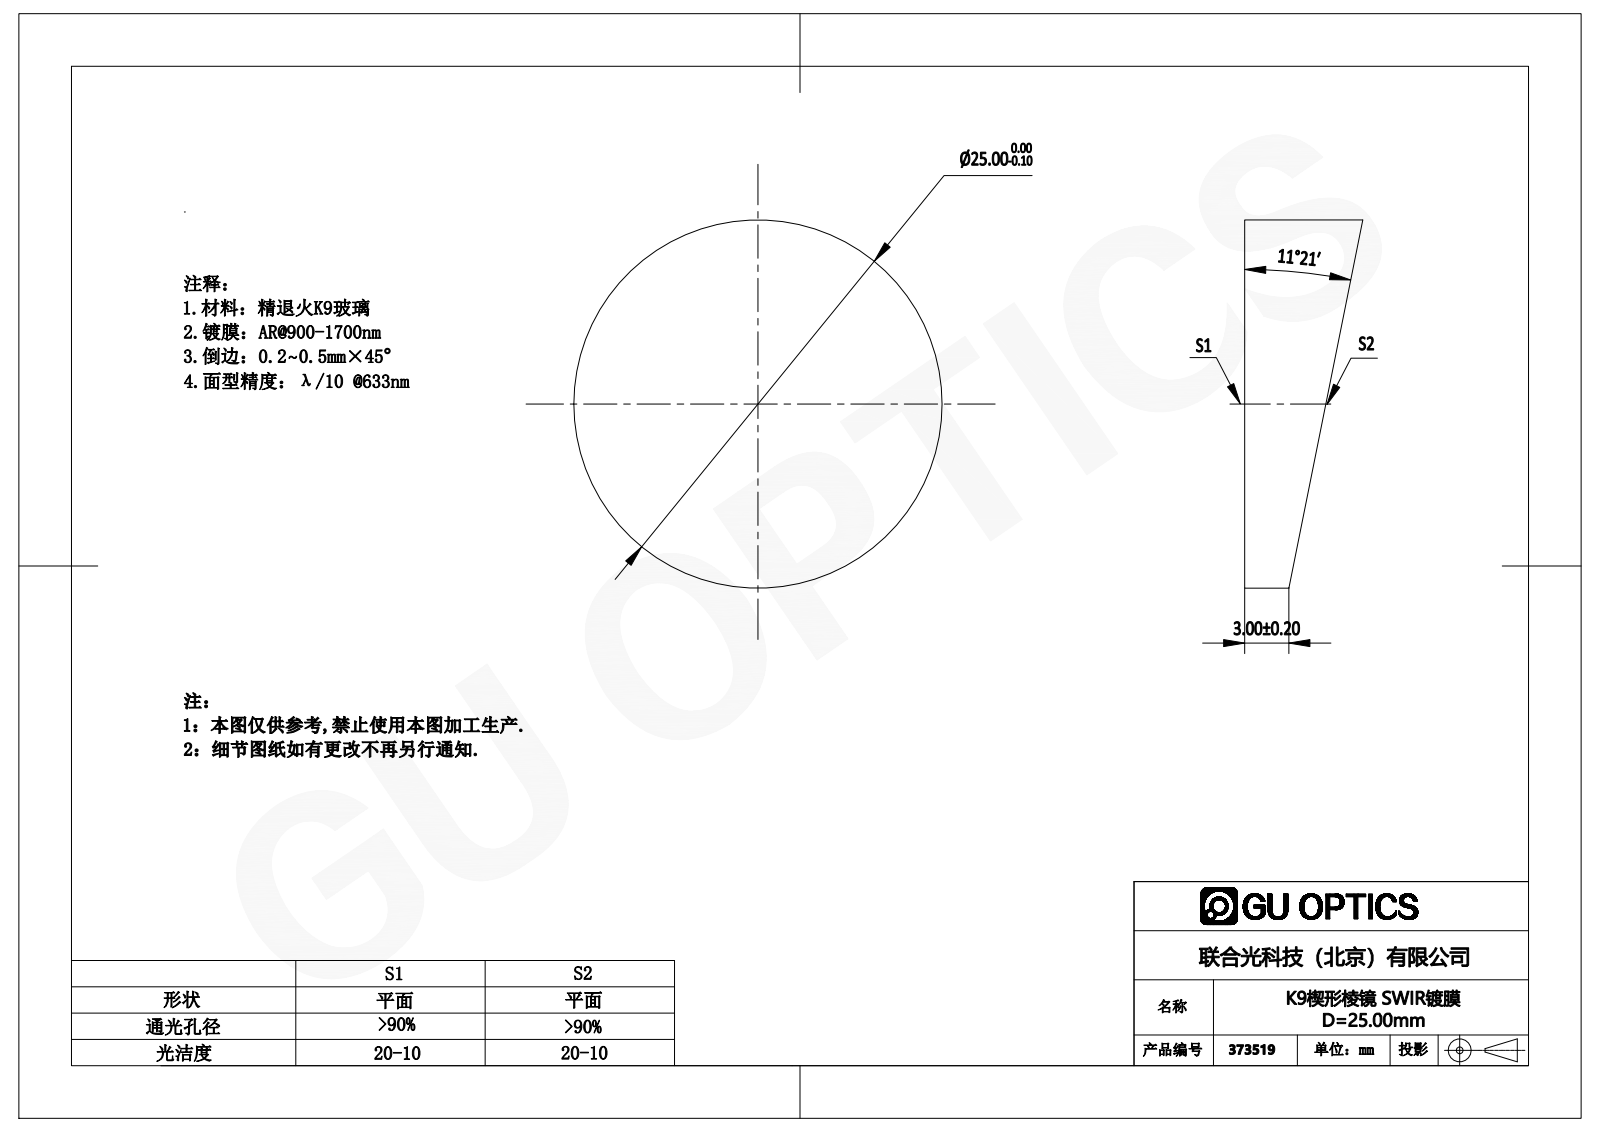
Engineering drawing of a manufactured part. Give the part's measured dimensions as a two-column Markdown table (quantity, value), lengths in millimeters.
| quantity | value |
| --- | --- |
| part name | 373516 |
| STEP written by | SolidWorks 2016 (CONFIG_CONTROL_DESIGN) |
| units | millimeters |
| bodies | 1 solid, 4 faces (2 planar, 2 cylindrical, 0 other) |
| overall size | 25 × 25 × 8.02 |
| volume | 2 704 mm³ |
| surface area | 1 424 mm² |
| round bosses / shafts (diameter × count) | 25 × 1 |
